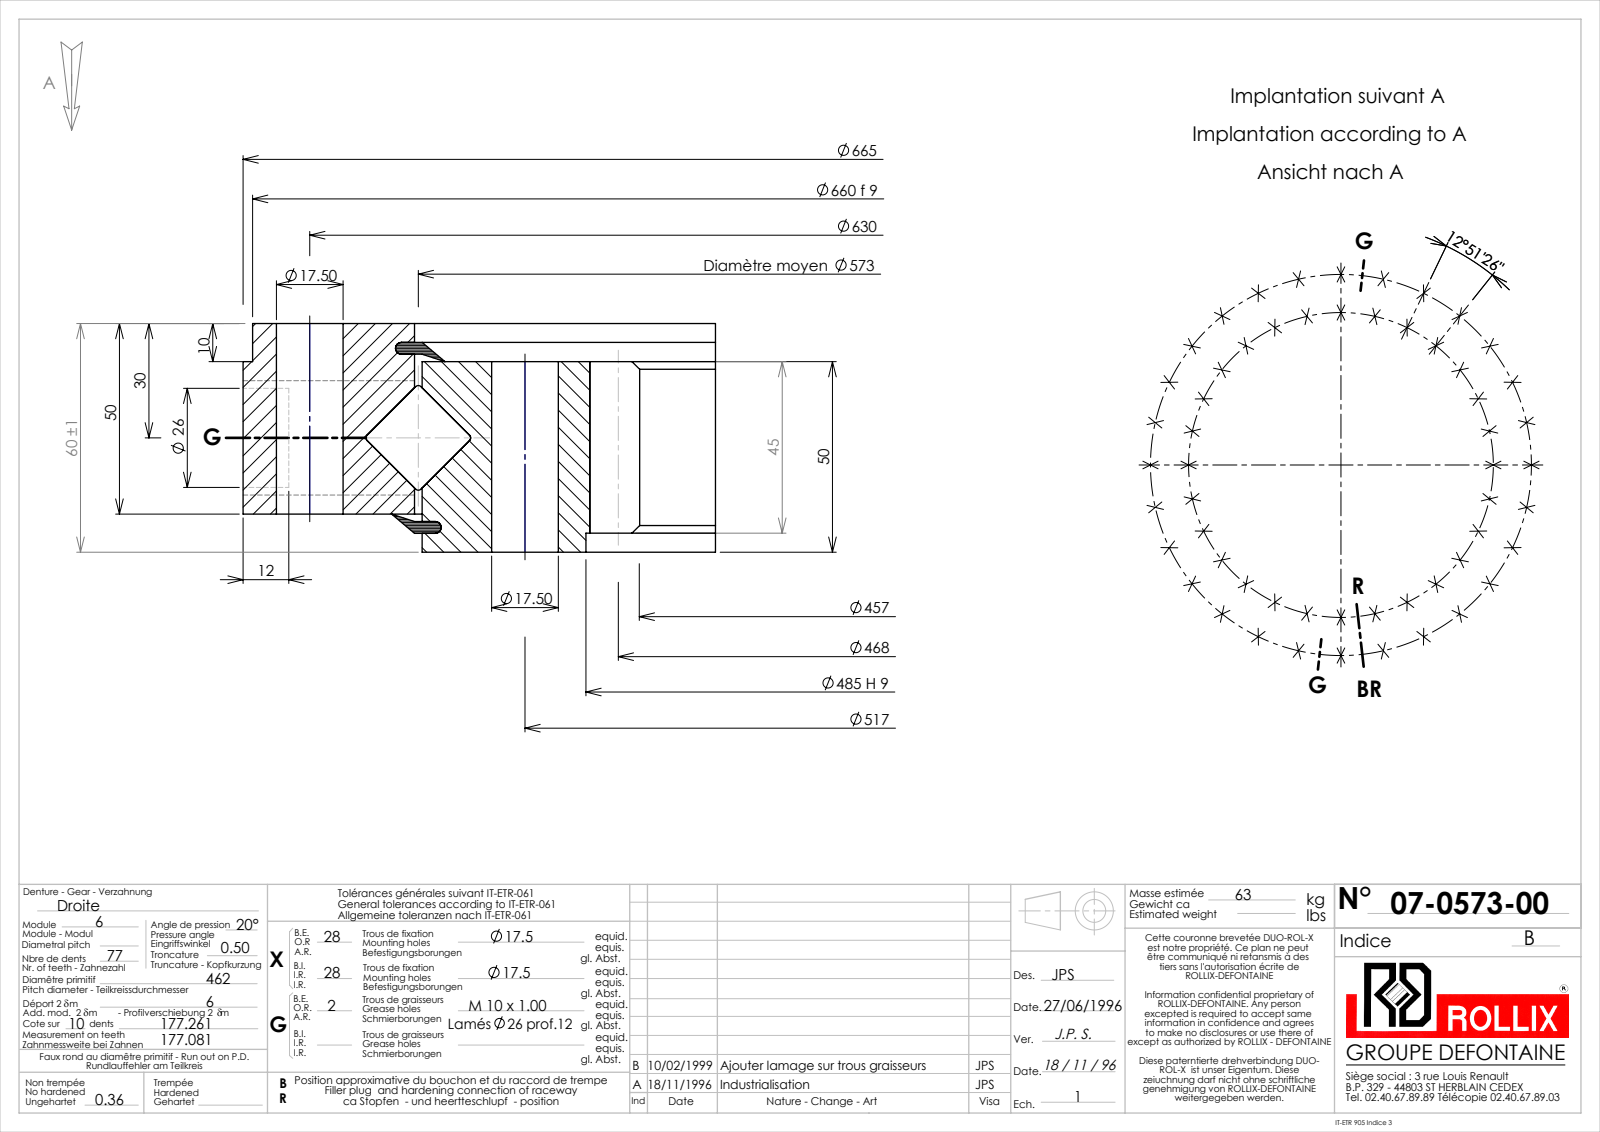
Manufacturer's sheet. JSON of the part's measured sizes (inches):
{"part_name": "07-0573-00", "step_written_by": "SolidWorks 2016 (CONFIG_CONTROL_DESIGN)", "units": "inches", "bodies": {"solids": 5, "faces": 664, "planar": 172, "cylindrical": 295, "other": 197}, "overall_size": [26.181, 26.181, 2.362], "volume_in3": 438.3, "surface_area_in2": 1657, "round_holes": [[0.689, 56], [0.354, 2], [1.024, 2], [19.094, 1], [22.638, 1]], "round_bosses_or_shafts": [[26.181, 1], [25.984, 1], [22.48, 1], [0.787, 1]], "partial_cylinders_radius": [[8.996, 1], [9.508, 1]], "face_to_face_distances": [0.394, 1.969, 1.575, 2.362, 0.195, 2.167, 0.199, 1.774, 0.317, 2.045], "hole_center_spacings": [4.529, 6.722, 8.831, 10.177, 10.829, 18.339, 20.226, 2.279]}
